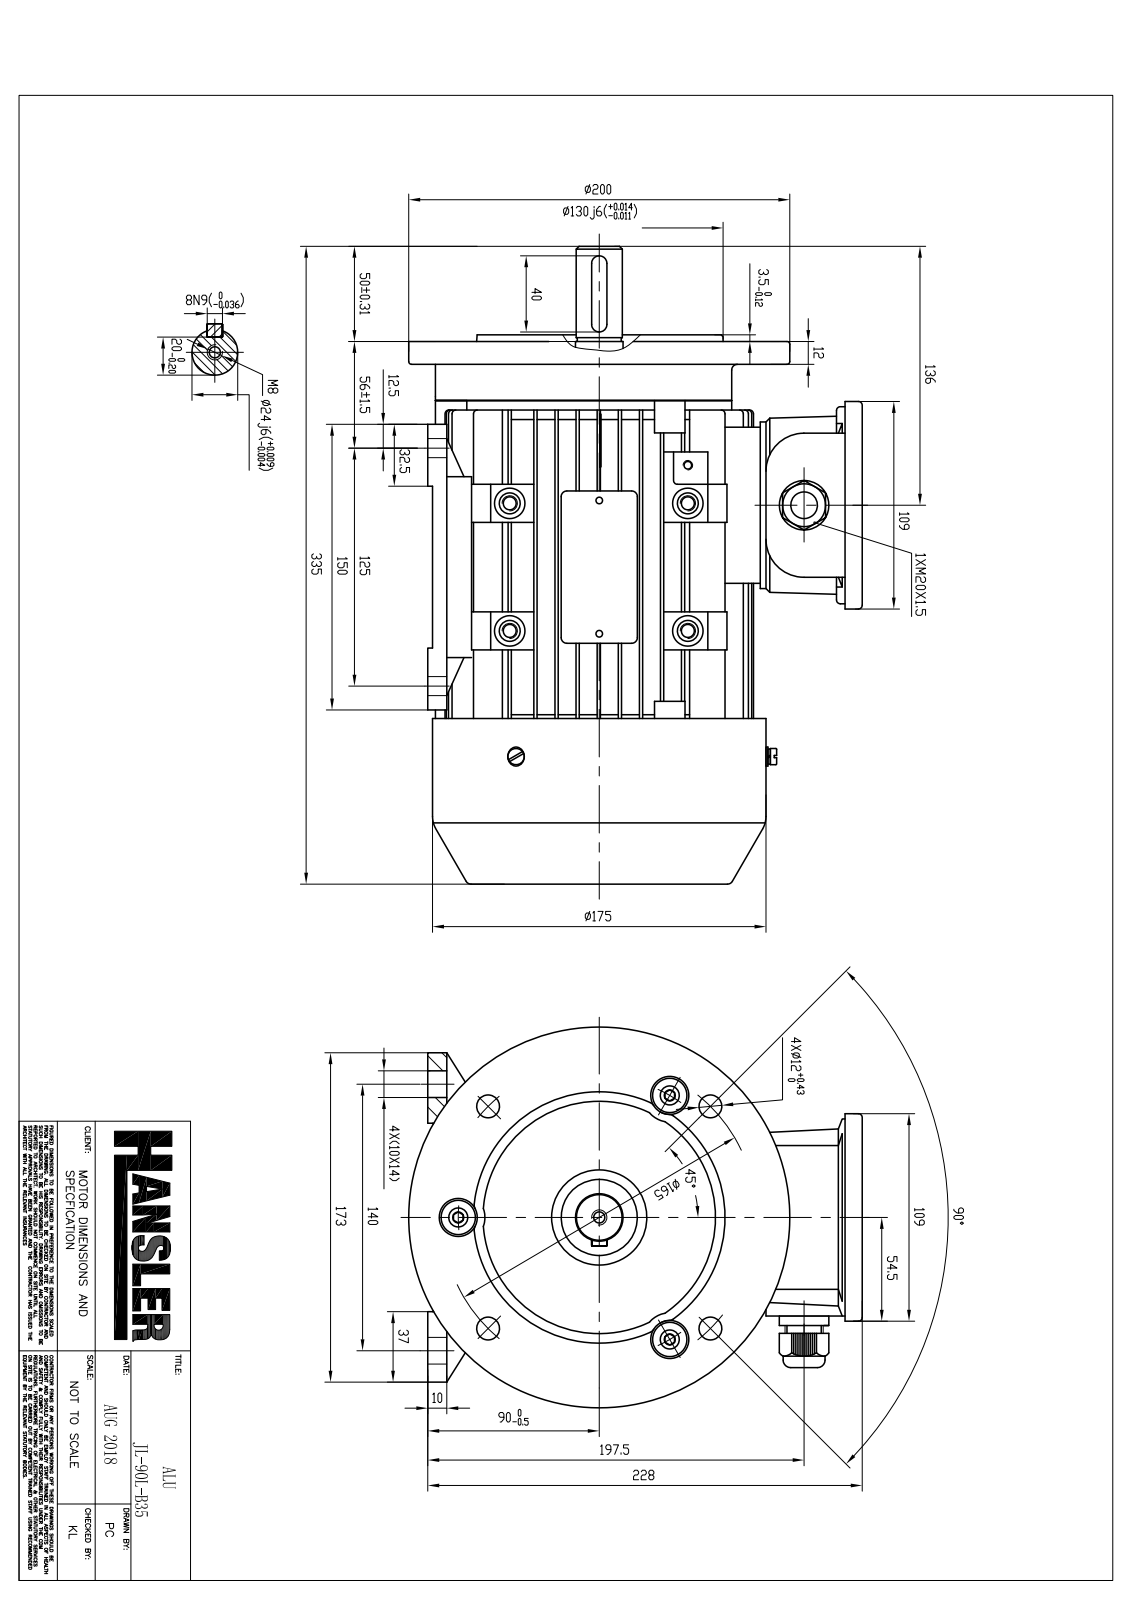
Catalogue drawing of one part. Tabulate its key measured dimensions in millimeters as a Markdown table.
| quantity | value |
| --- | --- |
| part name | JL-90L-B35 |
| STEP written by | SIEMENS PLM Software NX 12.0 (AP203_CONFIGURATION_CONTROLLED_3D_DESIGN_OF_MECHANICAL_PARTS_AND_ASSEMBLIES_MIM_LF) |
| units | millimeters |
| bodies | 51 solids, 4429 faces (2714 planar, 1308 cylindrical, 407 other) |
| overall size | 335 × 240.5 × 200 |
| volume | 1 507 000 mm³ |
| surface area | 934 234 mm² |
| round holes (diameter × count) | 4 × 13, 5 × 11, 5.8 × 10, 8 × 10, 12 × 8, 16 × 8, 4.8 × 4, 5.25 × 4, 5.3 × 4, 8.58 × 4, 9 × 4, 6 × 3 |
| round bosses / shafts (diameter × count) | 11 × 8, 4.48 × 8, 10 × 7, 15 × 4, 14.79 × 4, 13 × 4, 12 × 4, 7.85 × 4 |
| partial cylindrical surfaces (radius × count) | 0.5 × 464, 1 × 72, 2 × 69, 3 × 31, 4 × 19, 0.75 × 16, 5 × 16, 7 × 8 |
| main face-to-face distances | 1.7, 11.08, 44.32, 5, 22.16, 2.5, 9.38, 33.24, 2, 3 |
| hole center spacings | 35.51, 50.8, 57.1, 72.54, 77.07, 22, 15, 15.56 |
